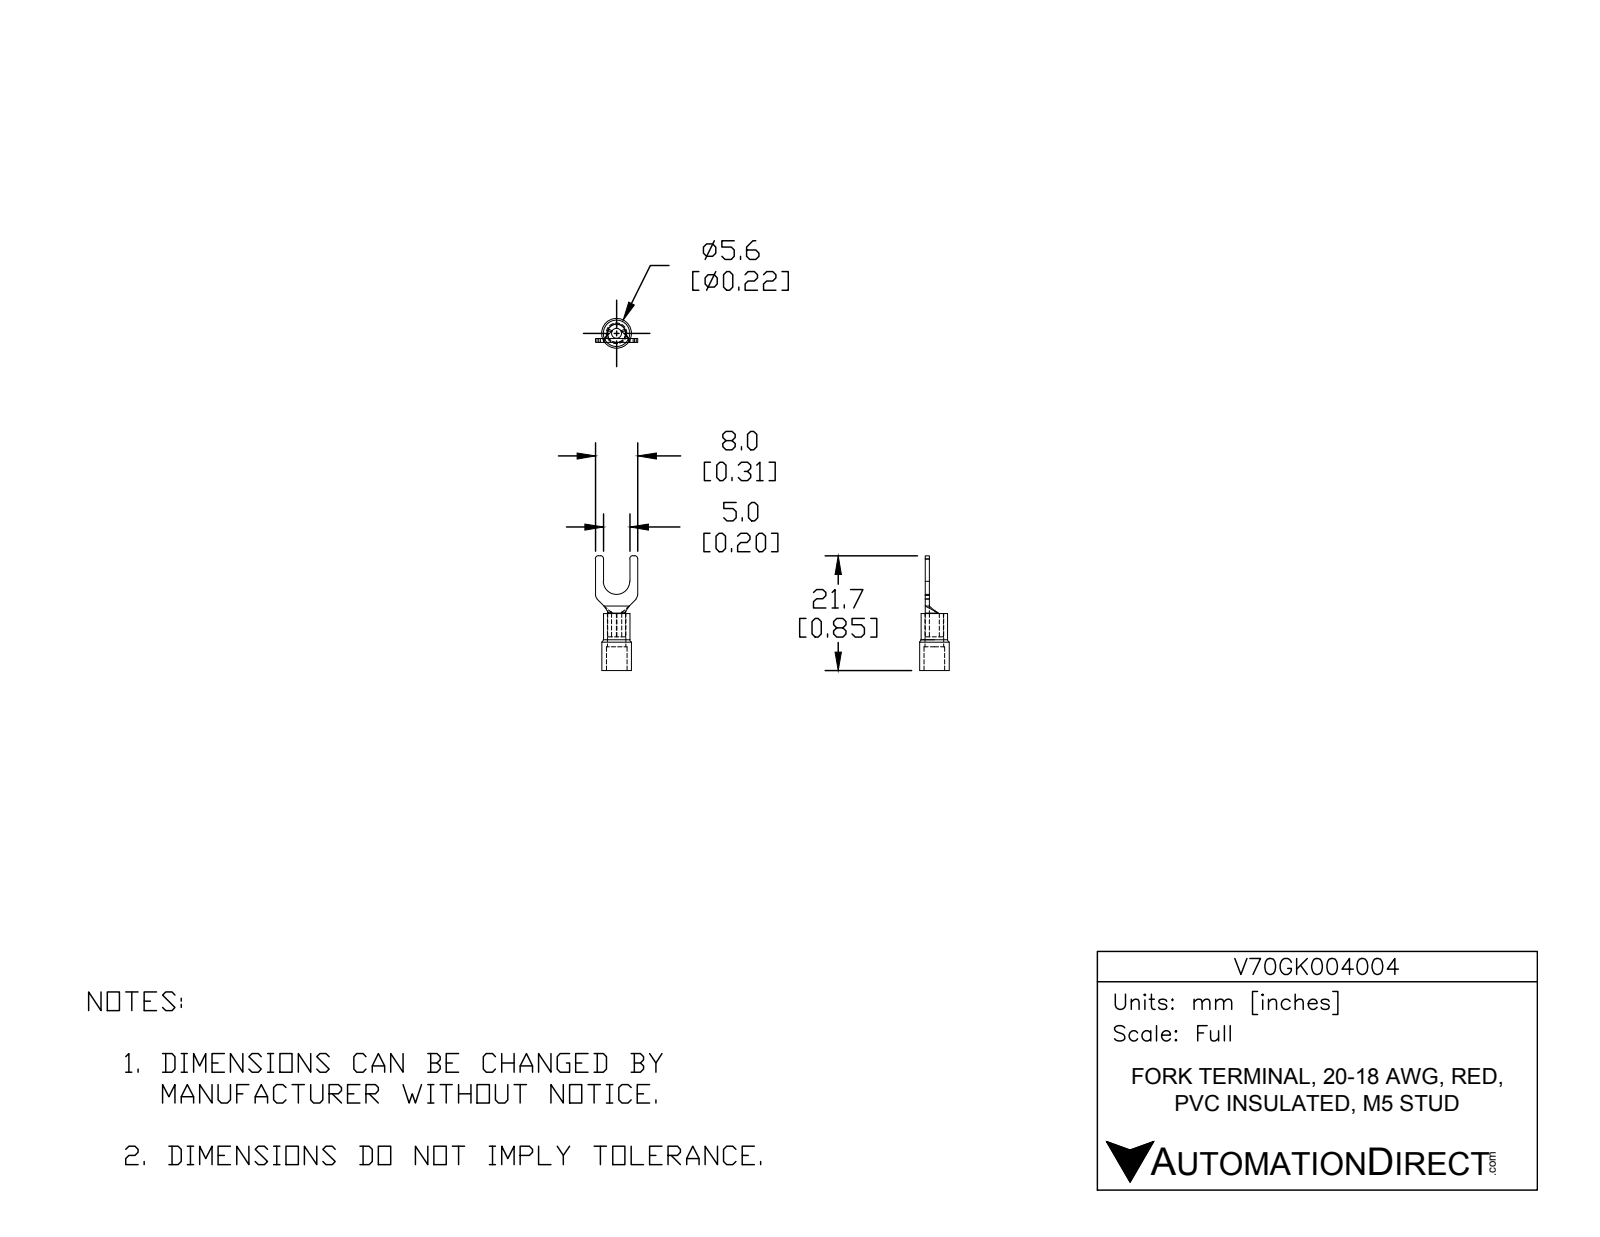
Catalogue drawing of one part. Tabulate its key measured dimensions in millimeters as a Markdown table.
| quantity | value |
| --- | --- |
| part name | V70GK004004 |
| STEP written by | SolidWorks 2017 (AUTOMOTIVE_DESIGN) |
| units | millimeters |
| bodies | 2 solids, 47 faces (18 planar, 21 cylindrical, 8 other) |
| overall size | 21.7 × 8 × 5.6 |
| volume | 186 mm³ |
| surface area | 544 mm² |
| round holes (diameter × count) | 1.91 × 1, 3.51 × 1, 3.9 × 1 |
| round bosses / shafts (diameter × count) | 5.6 × 1, 5 × 1, 3.41 × 1 |
| partial cylindrical surfaces (radius × count) | 0.6 × 4, 1 × 2, 2.5 × 1 |
| main face-to-face distances | 0.76, 10.8, 3.95, 4.05, 1.5, 6.5, 2.45, 2.55, 6.4, 4.4 |
